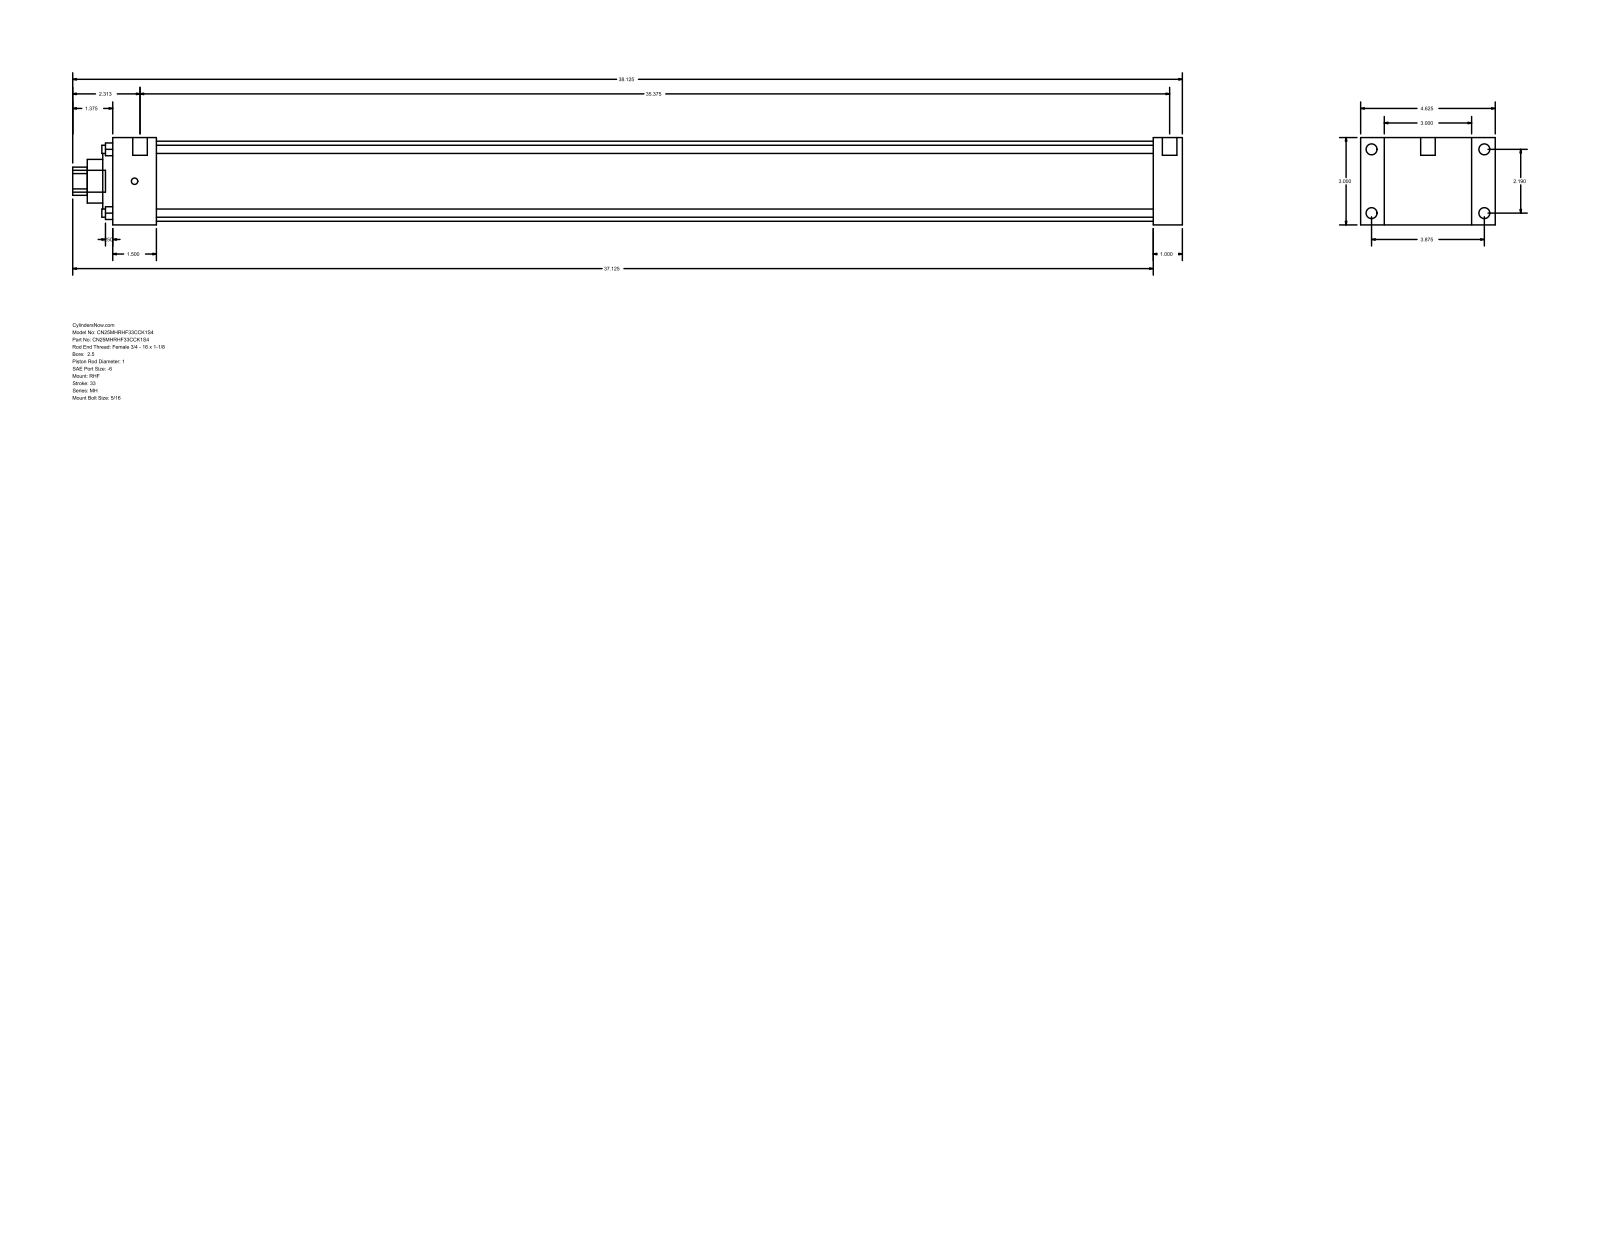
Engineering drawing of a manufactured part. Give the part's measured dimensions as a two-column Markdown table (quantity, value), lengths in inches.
| quantity | value |
| --- | --- |
| part name | MH_RHF__0250_1 |
| STEP written by | GSSL Pune (CONFIG_CONTROL_DESIGN) |
| units | inches |
| bodies | 0 solids, 90 faces (61 planar, 29 cylindrical, 0 other) |
| overall size | 38.125 × 4.625 × 3 |
| round holes (diameter × count) | 0.281 × 4, 1 × 1, 1.5 × 1, 2.375 × 1, 2.75 × 1 |
| round bosses / shafts (diameter × count) | 0.375 × 4, 0.219 × 4, 0.5 × 2, 0.75 × 1 |
| partial cylindrical surfaces (radius × count) | 0.484 × 1 |
| main face-to-face distances | 3, 1, 0.813, 3.813, 35.75, 36.75, 4.625, 1.5, 34.25, 35.25 |
| hole center spacings | 1.548, 2.19, 3.097 |
